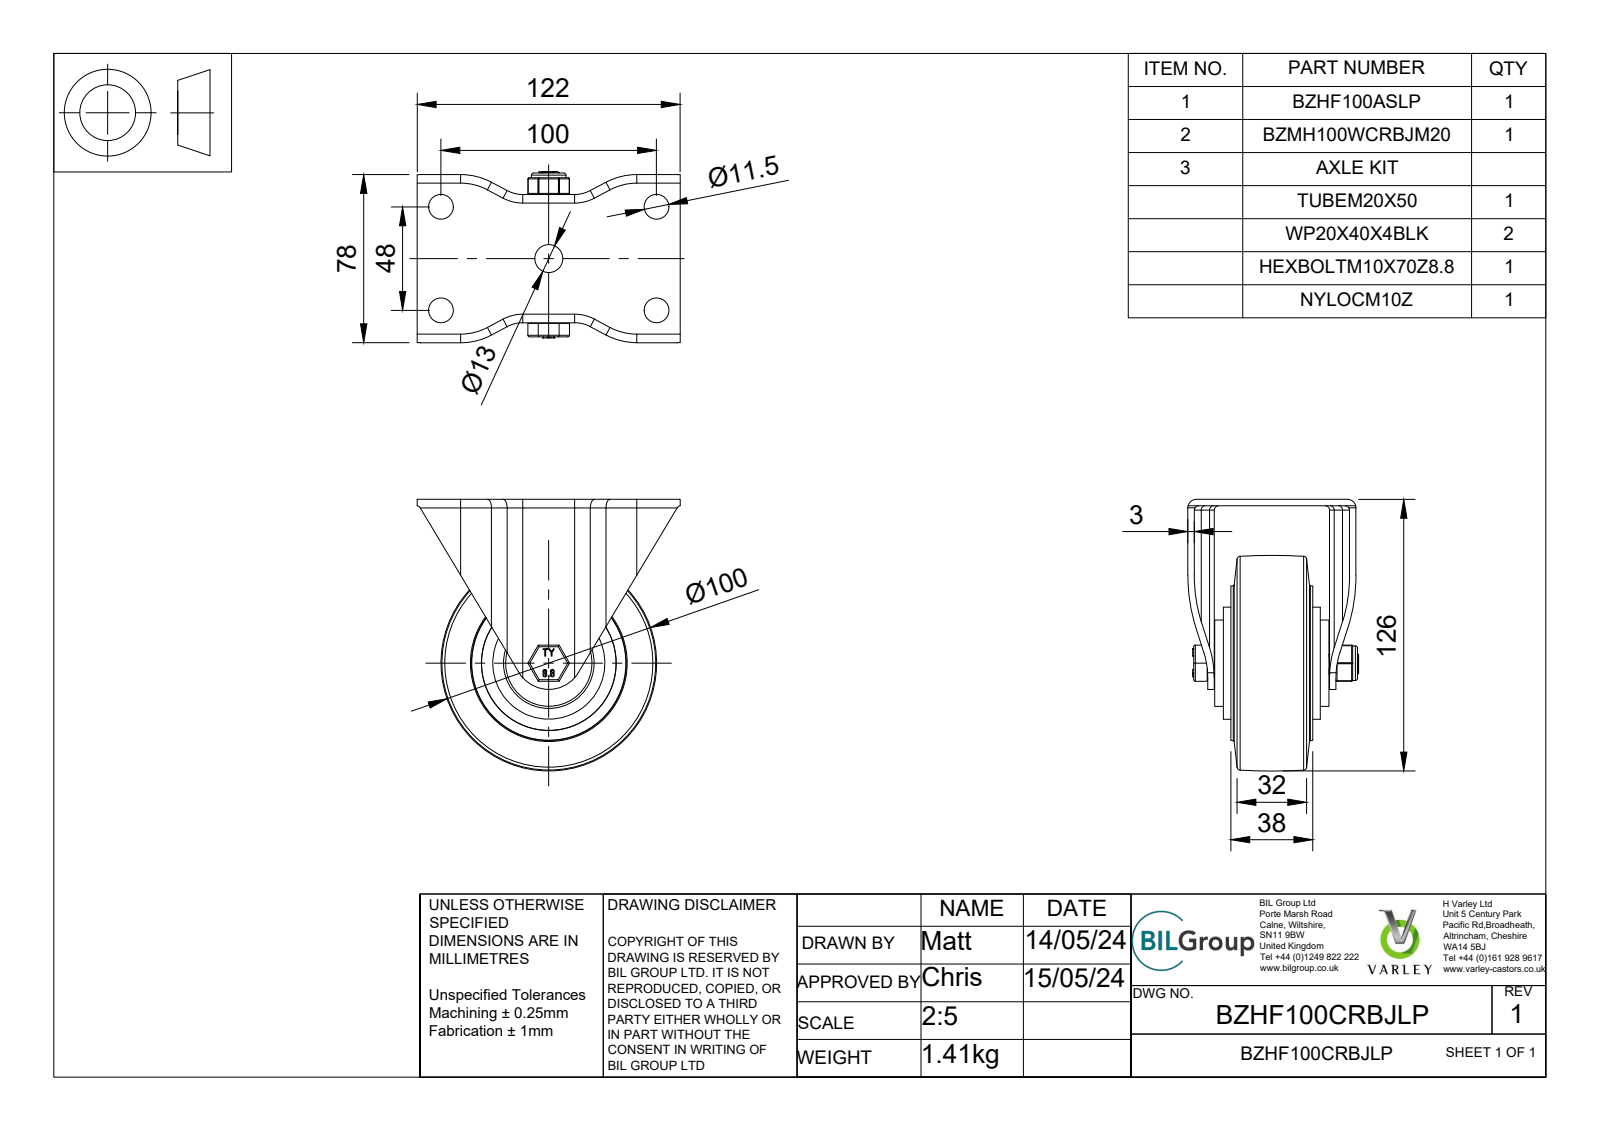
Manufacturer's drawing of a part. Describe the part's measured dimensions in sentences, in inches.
The part is named "BZHF100CRBJLP v3; BZMH100WCRBJM20 v1; ELASTIC RUBBER TYRE; CAST IRON RIM (+7 more)". Its 3-D file was written by "Autodesk Translation Framework v13.14.0.145 (AUTOMOTIVE_DESIGN)". It is 38 solids with 1180 faces: 432 planar, 238 cylindrical and 510 other. Overall it measures 4.961 by 4.803 by 3.12 inches. Its volume is 20.69 cubic inches and its surface area 202.4 square inches. Round holes: 4 of diameter 0.453, 1 of diameter 0.394, 1 of diameter 0.413, 1 of diameter 0.425, 1 of diameter 0.472, 1 of diameter 0.512, 1 of diameter 0.787, 1 of diameter 0.827, 1 of diameter 0.984, 1 of diameter 1.024, 1 of diameter 1.378, 1 of diameter 1.417. Round bosses or shafts: 18 of diameter 0.315, 1 of diameter 2.047, 1 of diameter 1.575, 1 of diameter 1.457, 1 of diameter 1.063, 1 of diameter 0.945, 1 of diameter 0.783, 1 of diameter 0.63. Partial cylindrical surfaces (rounded edges, fillets, slot ends): 18 of radius 0.02, 10 of radius 0.079, 8 of radius 0.157, 6 of radius 0.03, 4 of radius 0.61, 4 of radius 0.728, 4 of radius 1.083, 4 of radius 1.201. The main face-to-face distances are 0.118, 0.285, 2.057, 0.423, 1.919, 0.138, 1.634, 0.167, 2.224, 0.305. The hole center spacings are 2.183, 1.89, 3.937, 4.367.
